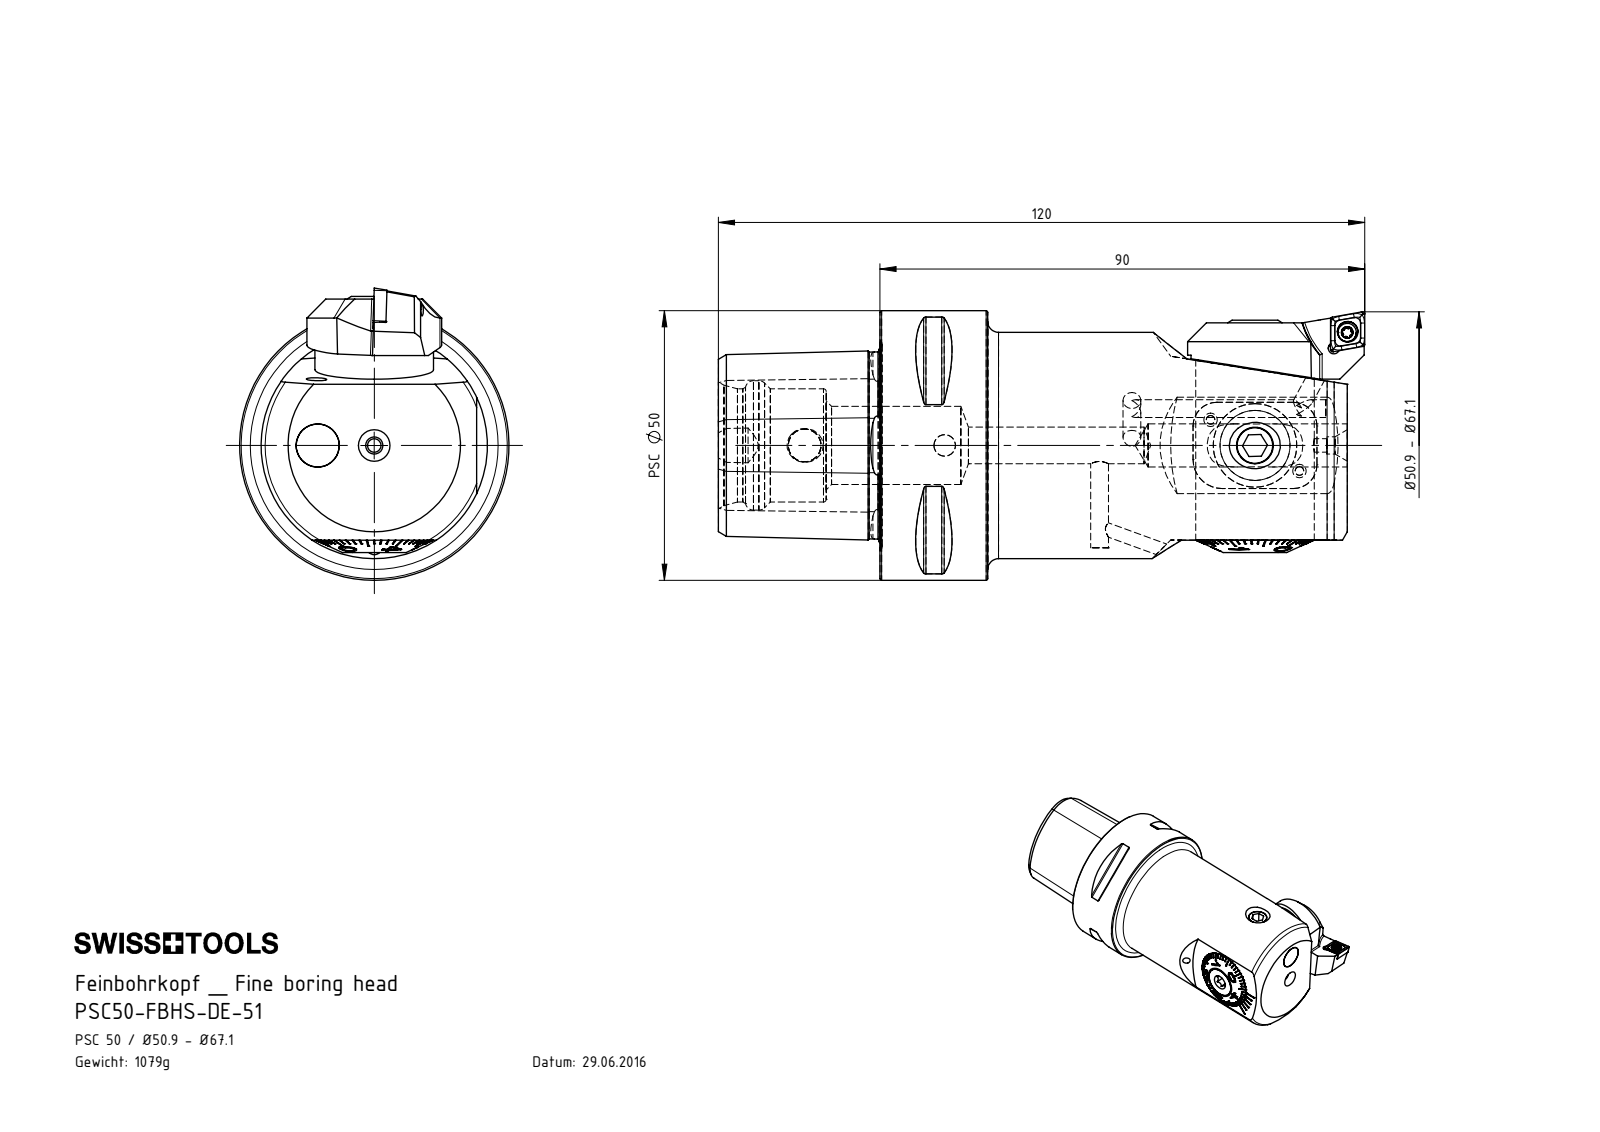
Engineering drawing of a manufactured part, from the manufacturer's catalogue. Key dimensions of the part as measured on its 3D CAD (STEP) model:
Part name (STEP PRODUCT): F42-ER1.101.020_A; ISO 4762 - M2 x 6; PEF-DA1.011.017_A; ISO 4026 - M8 x 6 (+8 more)
STEP written by: SolidWorks 2017 (AUTOMOTIVE_DESIGN)
Units: millimetres
Bodies: 19 solids, 742 faces (402 planar, 127 cylindrical, 213 other)
Overall size (bounding box): 116.75 × 52.65 × 50
Volume: 135 766 mm³ · Surface area: 37 177 mm²
Round holes (diameter × count): ⌀3.3 ×4, ⌀6.8 ×3, ⌀1.6 ×2, ⌀2.2 ×2, ⌀2.5 ×2, ⌀4.2 ×2, ⌀3 ×1, ⌀3.2 ×1, ⌀3.9 ×1, ⌀4 ×1, ⌀6 ×1, ⌀6.1 ×1
Round bosses / shafts (diameter × count): ⌀1.9 ×6, ⌀8 ×2, ⌀3.8 ×2, ⌀2 ×2, ⌀50 ×1, ⌀42 ×1, ⌀22 ×1, ⌀21.98 ×1
Partial cylindrical surfaces — rounded edges, fillets, slot ends (radius × count): R0.5 ×11, R1.1 ×6, R1.2 ×6, R3.2 ×5, R2 ×4, R4.5 ×4, R4.4 ×3, R3.1 ×2
Main face-to-face distances: 86.75, 30, 4, 4.4, 20, 2.3, 1.1, 2.2, 4.5, 10
Hole centre spacings: 9.52, 7.67, 10.5, 15.58, 19.04, 26, 28.85, 49.58
